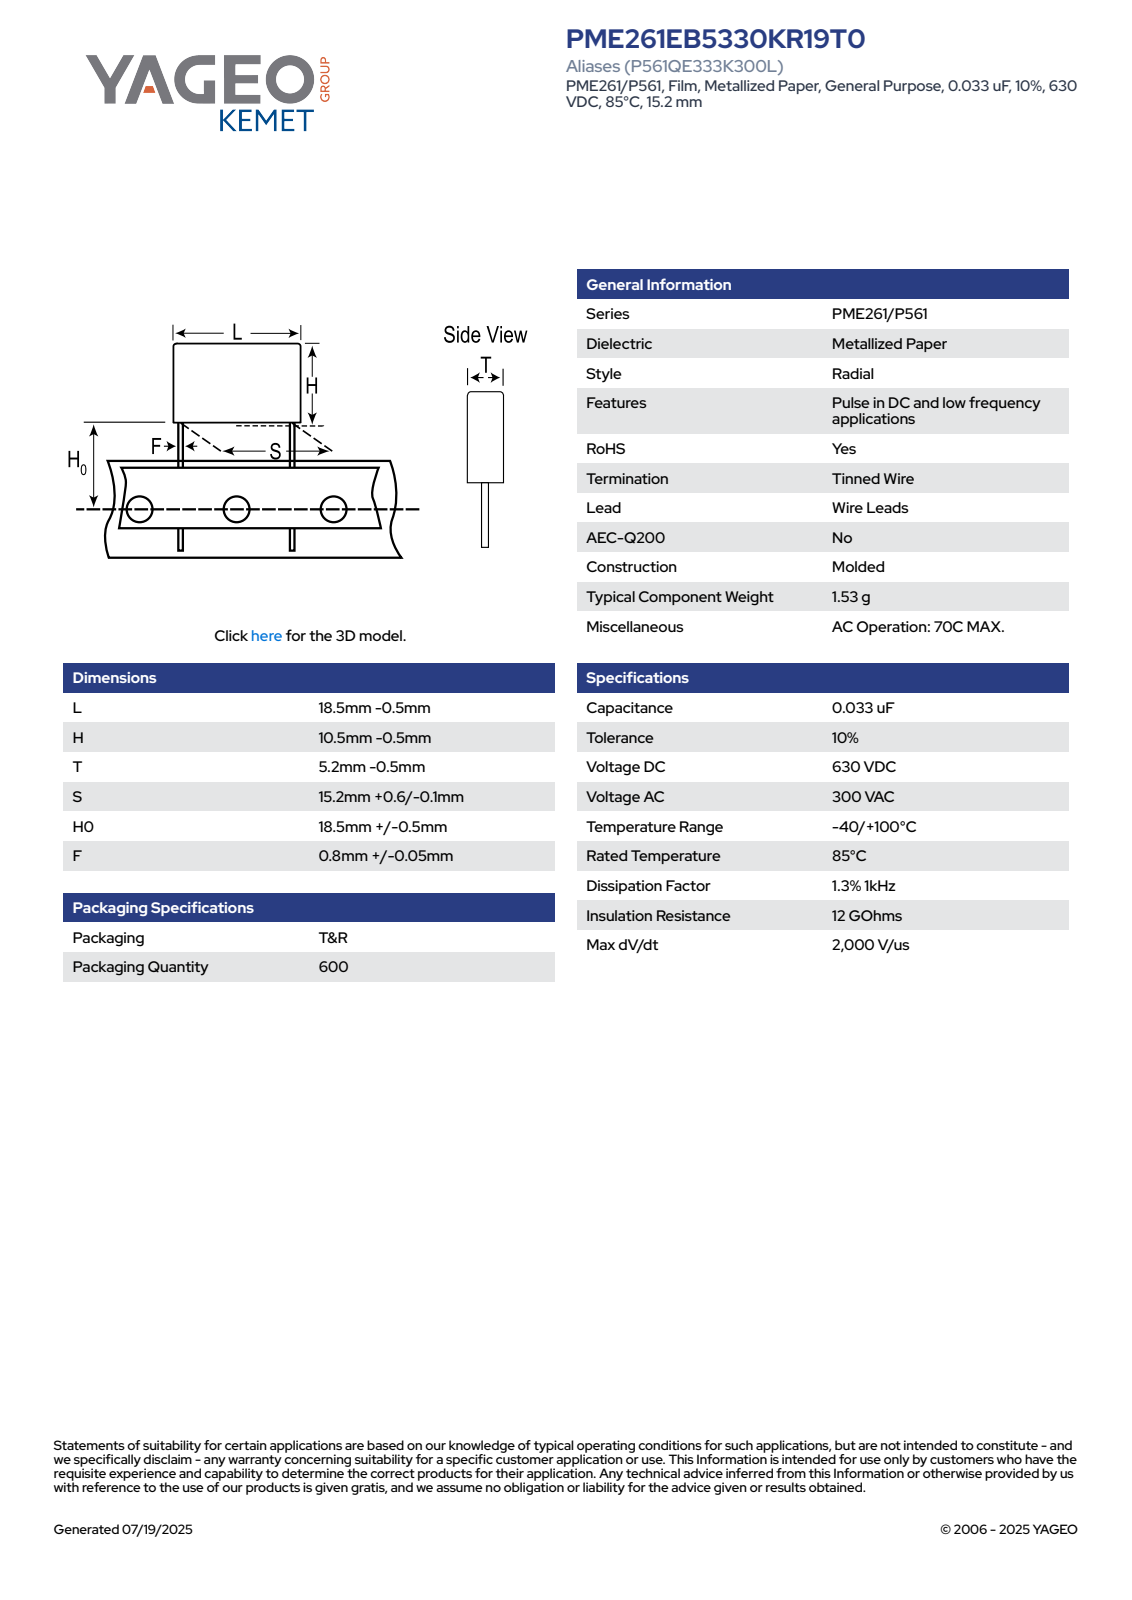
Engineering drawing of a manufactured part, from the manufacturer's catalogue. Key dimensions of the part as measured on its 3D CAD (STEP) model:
Part name (STEP PRODUCT): CFR_MOLDED_18.5X10.5X5.2_L18H10T4.7S15.2H019F0.85
STEP written by: SolidWorks 2014 (AUTOMOTIVE_DESIGN)
Units: millimetres
Bodies: 4 solids, 73 faces (65 planar, 8 cylindrical, 0 other)
Overall size (bounding box): 29 × 18 × 4.71
Volume: 865 mm³ · Surface area: 730 mm²
Round bosses / shafts (diameter × count): ⌀0.85 ×2
Partial cylindrical surfaces — rounded edges, fillets, slot ends (radius × count): R0.5 ×4
Main face-to-face distances: 4.7, 10, 18, 4.71, 19, 29, 4.19, 5.81, 24.81, 23.19
